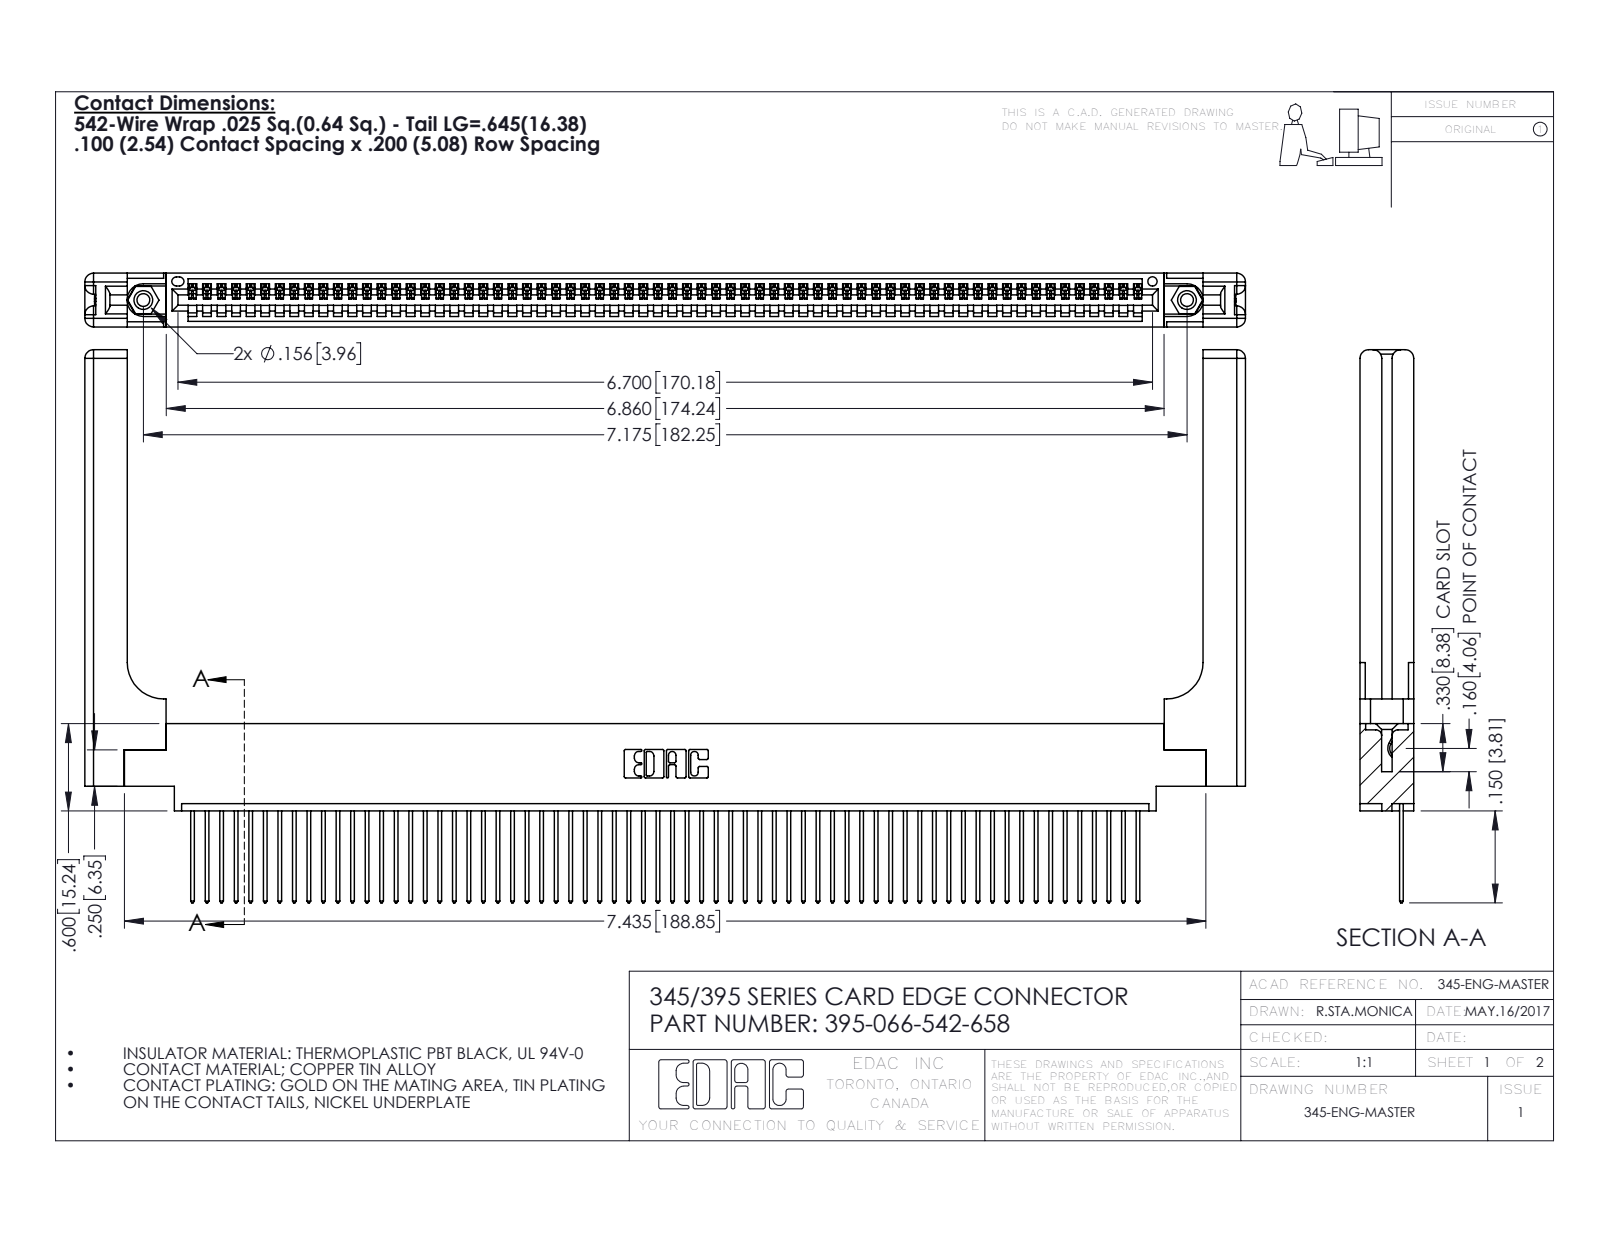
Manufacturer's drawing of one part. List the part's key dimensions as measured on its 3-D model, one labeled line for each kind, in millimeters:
Part name (STEP PRODUCT): 345-220-058_345-220-058; 345-292-001_345-293-142; 395-066-542-658; 345-250-001_345-250-001-102 (+1 more)
STEP written by: SolidWorks 2016 (CONFIG_CONTROL_DESIGN)
Units: millimetres
Bodies: 71 solids, 4214 faces (2872 planar, 1282 cylindrical, 60 other)
Overall size (bounding box): 202.7 × 96.6 × 9.4
Volume: 27 990 mm³ · Surface area: 32 570 mm²
Round holes (diameter × count): ⌀2.3 ×2, ⌀3.2 ×2, ⌀4 ×2, ⌀1.6 ×1
Round bosses / shafts (diameter × count): ⌀3.9 ×2
Partial cylindrical surfaces — rounded edges, fillets, slot ends (radius × count): R0.2 ×132, R0.3 ×132, R0.3 ×22, R1.5 ×16, R0.2 ×6, R0.8 ×6, R0.7 ×3, R0.8 ×2
Main face-to-face distances: 1.8, 7.6, 9.4, 2.5, 6.9, 0.6, 5.1, 5.7, 3.8, 3.8
Hole centre spacings: 6.9, 176.3, 182.2
